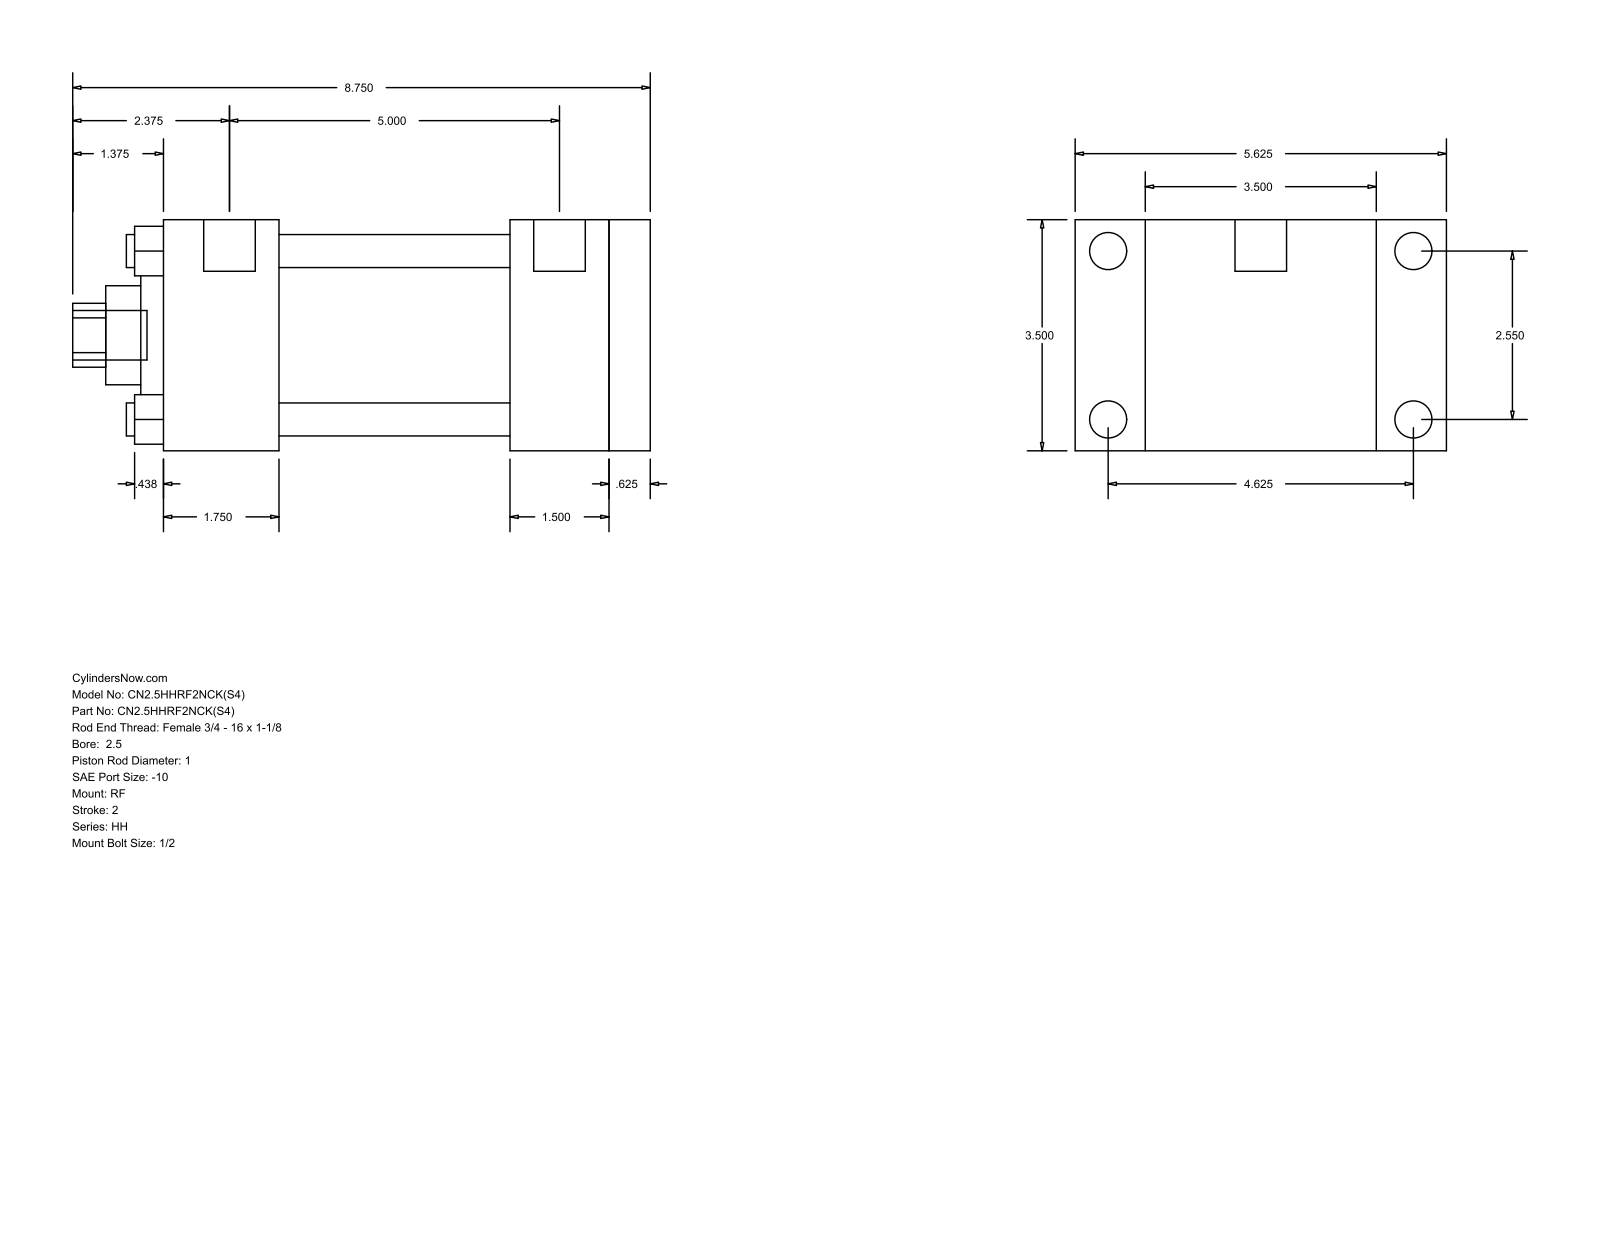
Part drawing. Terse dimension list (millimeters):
name: HH_RF__0250_1
written by: GSSL Pune (CONFIG_CONTROL_DESIGN)
unit: mm
bodies: 0 solids, 94 faces (65 planar, 29 cylindrical, 0 other)
size: 222.25 × 142.88 × 88.9
holes: 4× ⌀12.7, 1× ⌀25.4, 1× ⌀38.1, 1× ⌀60.33, 1× ⌀73.03
bosses: 4× ⌀14.3, 4× ⌀5.56, 2× ⌀19.84, 1× ⌀19.05
rounds: 1× R12.29
face distances: 88.9, 15.87, 171.46, 187.33, 44.46, 127, 142.87, 133.36, 38.1, 53.97
hole spacings: 45.79, 64.76, 91.58
